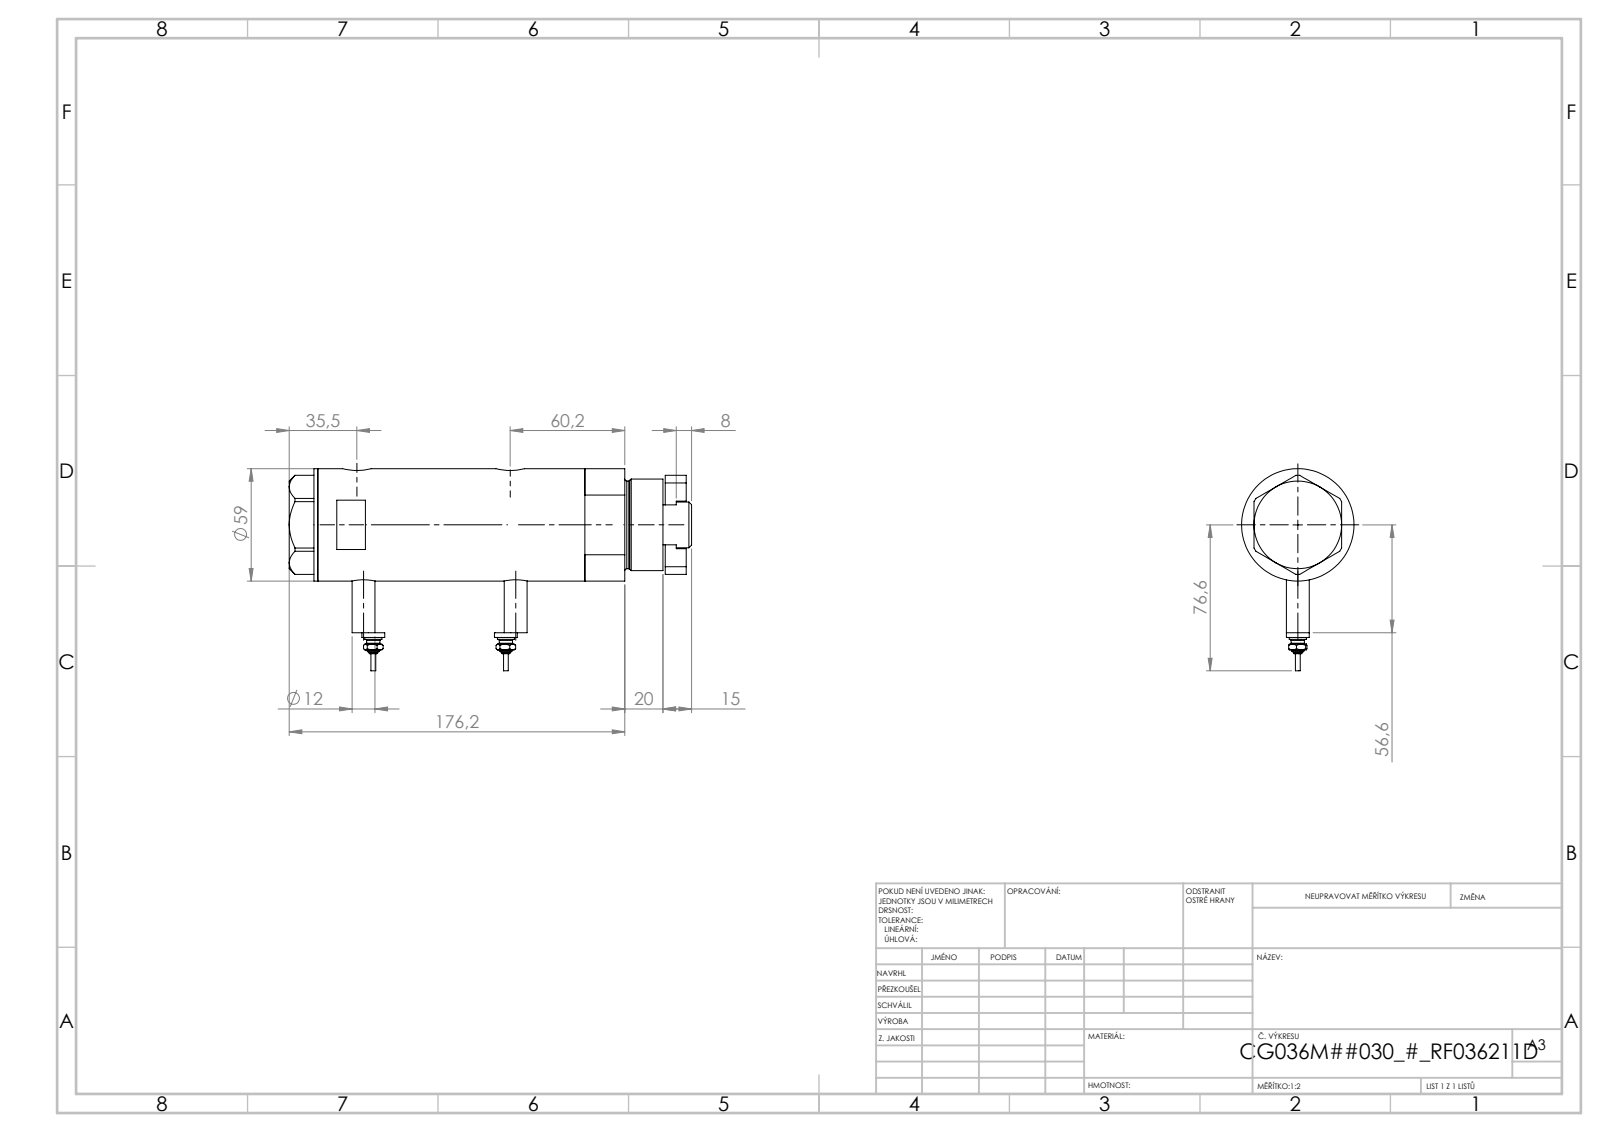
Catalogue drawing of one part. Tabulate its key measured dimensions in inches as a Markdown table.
| quantity | value |
| --- | --- |
| part name | V270CG_VC; V270CG_FRONT; V270CG_MIDDLE; V270CG_BACK (+2 more) |
| STEP written by | SolidWorks 2019 (CONFIG_CONTROL_DESIGN) |
| units | inches |
| bodies | 8 solids, 272 faces (105 planar, 93 cylindrical, 74 other) |
| overall size | 7.615 × 3.594 × 2.323 |
| volume | 27.18 in³ |
| surface area | 154 in² |
| round holes (diameter × count) | 0.24 × 4, 0.413 × 4, 0.197 × 2, 0.383 × 2, 0.492 × 2, 0.591 × 2, 0.335 × 1, 0.984 × 1, 1.043 × 1, 1.417 × 1, 1.575 × 1, 2.047 × 1 |
| round bosses / shafts (diameter × count) | 0.472 × 3, 0.354 × 2, 0.276 × 2, 0.171 × 2, 0.094 × 2, 2.323 × 1, 1.89 × 1, 1.811 × 1 |
| main face-to-face distances | 3.439, 0.925, 2.513, 0.591, 1.516, 4.029, 1.496, 7.024, 0.079, 6.434 |
| hole center spacings | 0.784, 0.114, 0.138, 0.472, 1.495, 1.568, 2.447, 2.561 |
